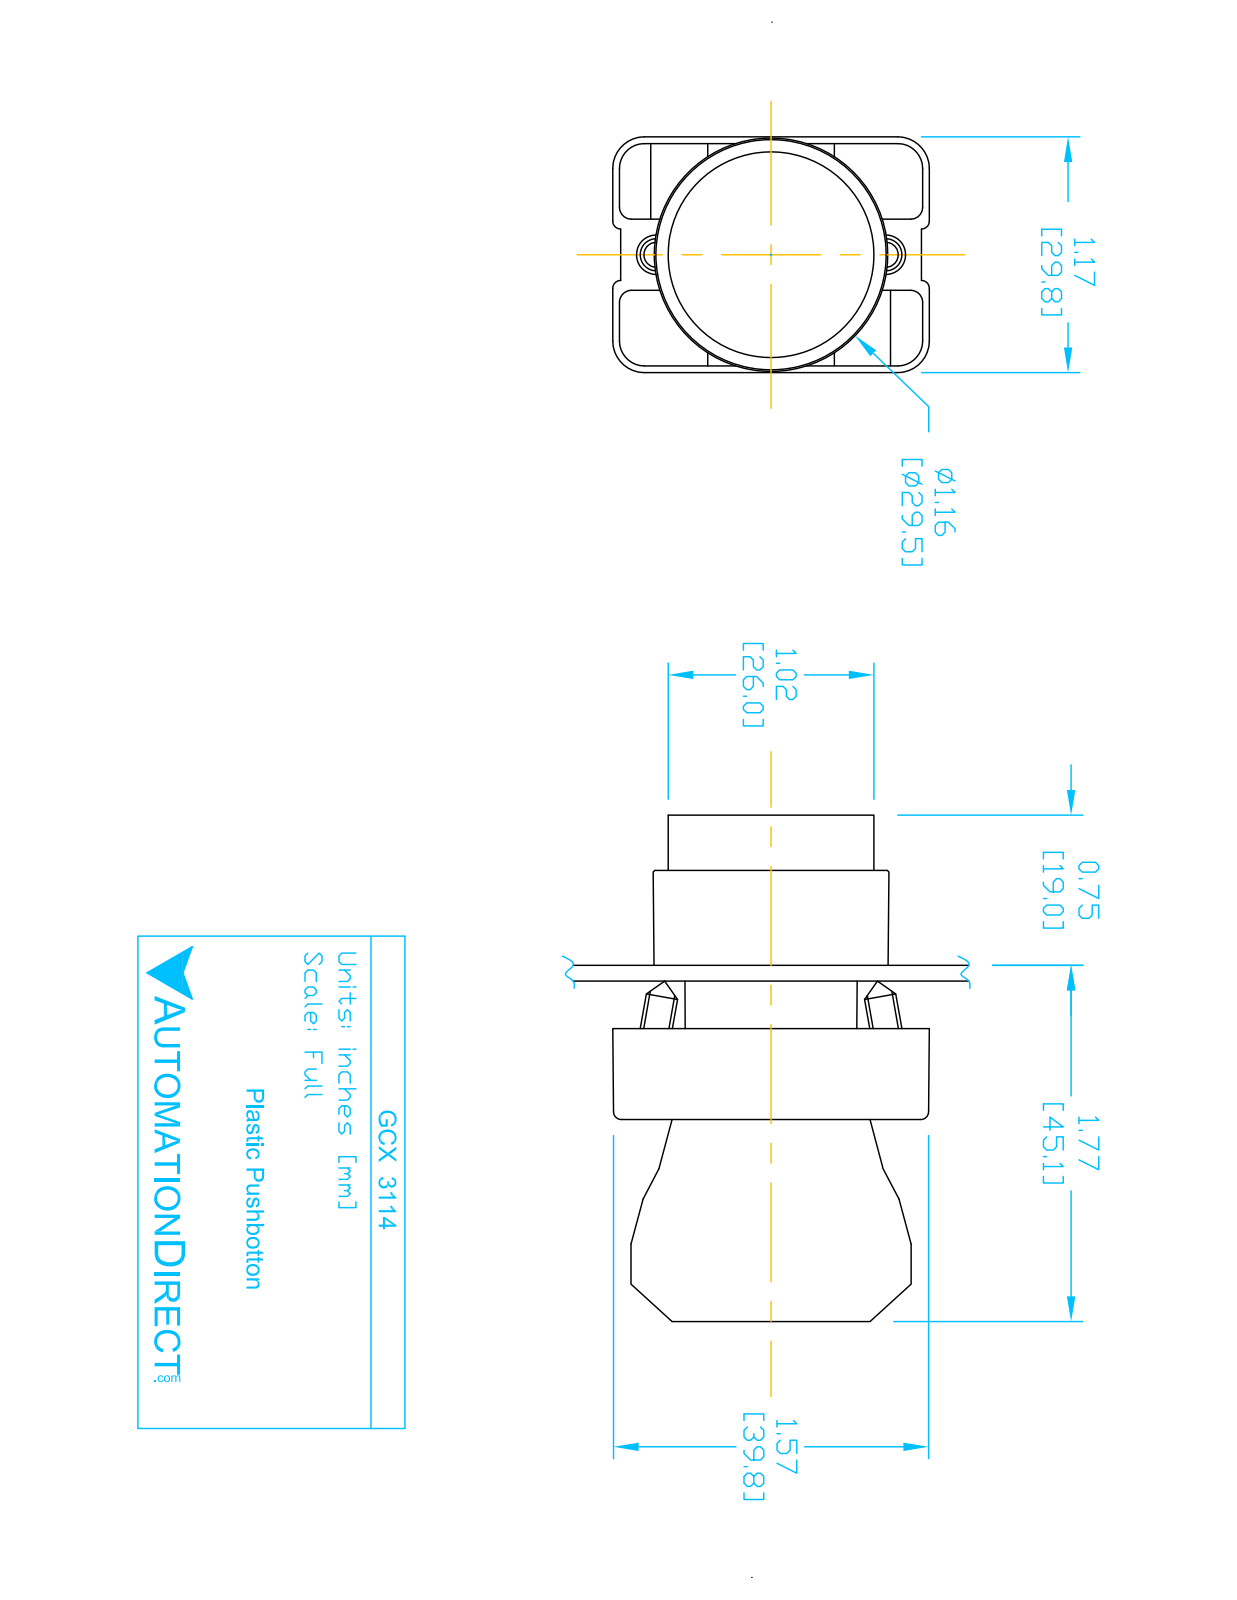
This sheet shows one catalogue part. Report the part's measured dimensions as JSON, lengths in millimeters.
{"part_name": "ecx1040; GCX3114; ECX3029-2; GCX3114 OPERATOR", "step_written_by": "SolidWorks 2016 (AUTOMOTIVE_DESIGN)", "units": "millimeters", "bodies": {"solids": 6, "faces": 383, "planar": 222, "cylindrical": 132, "other": 29}, "overall_size": [63.3, 40.2, 29.9], "volume_mm3": 25960, "surface_area_mm2": 17080, "round_holes": [[2, 2], [3.1, 2], [3.3, 2], [2.2, 1], [5, 1], [22.3, 1], [22.6, 1], [26, 1]], "round_bosses_or_shafts": [[4, 2], [29.8, 1], [25.5, 1], [24, 1], [21.7, 1], [19.8, 1]], "partial_cylinders_radius": [[1.5, 24], [1, 12], [3.1, 12], [4, 12], [1, 4], [3.3, 2], [0.5, 1], [1.6, 1]], "face_to_face_distances": [14.7, 0.8, 30.3, 0.8, 12, 18.3, 7, 17.5, 15.2, 29.5], "hole_center_spacings": [6, 13.8, 12, 12.4]}
